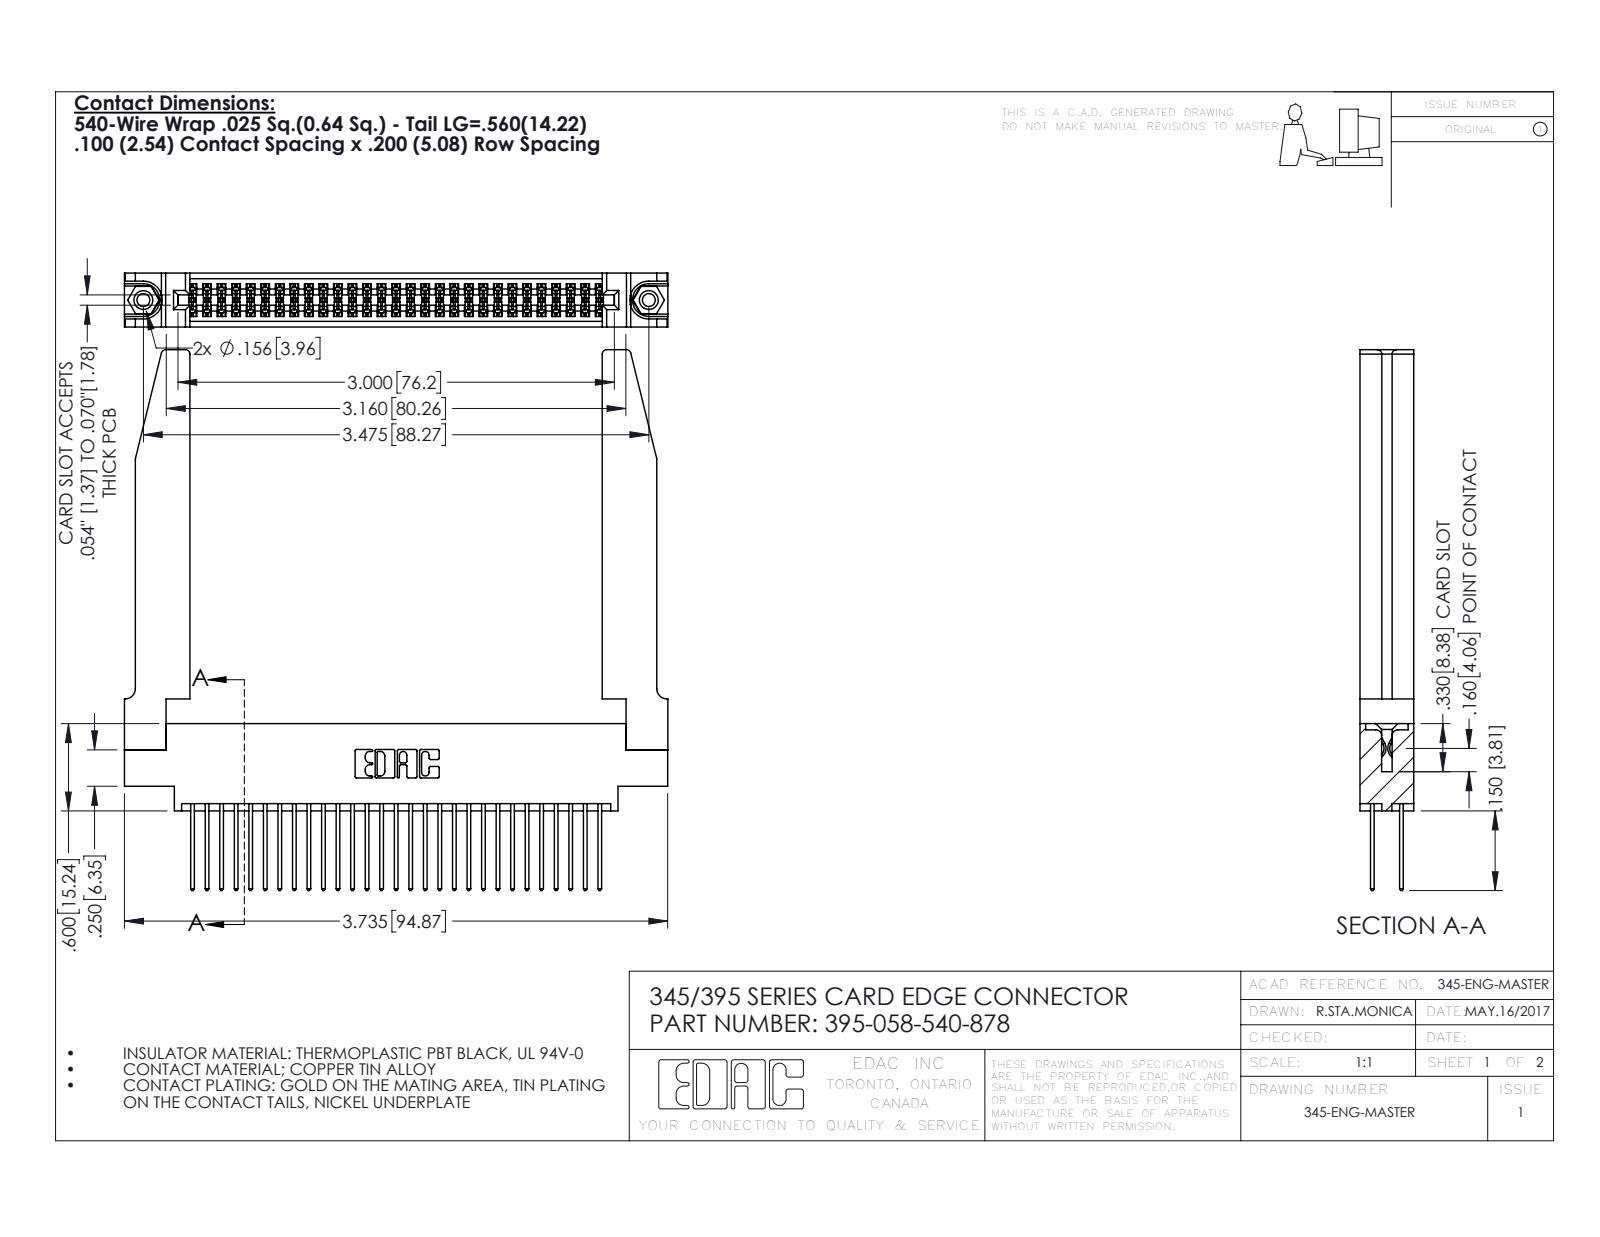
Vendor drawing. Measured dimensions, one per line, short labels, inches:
name: 345 Part_0.170 Offset - 0.156 Dia-TH; 345-250-001_345-250-001-102; 395-058-540-878; 345-292-001_345-293-140 (+1 more)
written by: SolidWorks 2016 (CONFIG_CONTROL_DESIGN)
unit: in
bodies: 63 solids, 3264 faces (2140 planar, 1072 cylindrical, 52 other)
size: 3.736 × 3.717 × 0.37
volume: 1.036 in³; area: 33.1 in²
holes: 2× ⌀0.089, 2× ⌀0.125, 2× ⌀0.156, 1× ⌀0.064
bosses: 2× ⌀0.155
rounds: 87× R0.006, 58× R0.01, 22× R0.01, 8× R0.03, 6× R0.007, 6× R0.031, 3× R0.026, 2× R0.014
face distances: 0.37, 0.072, 0.298, 0.098, 0.272, 0.025, 0.2, 0.225, 0.175, 0.148
hole spacings: 0.27, 3.24, 3.475
